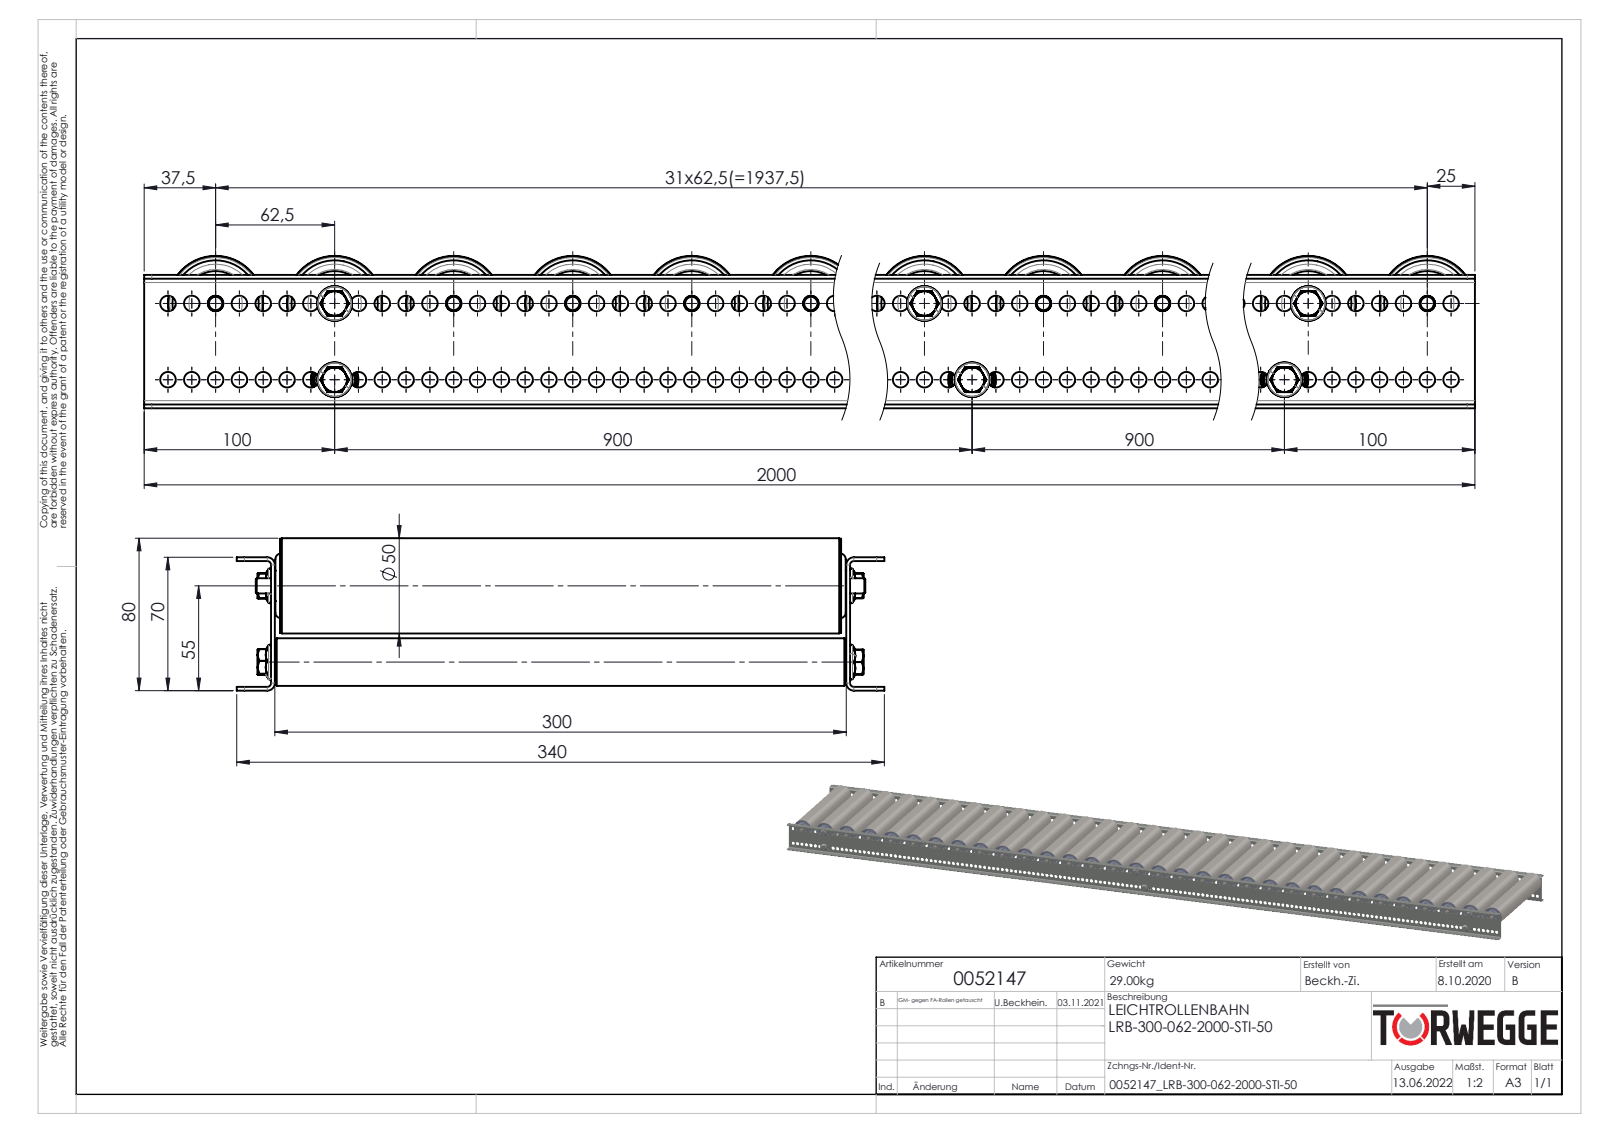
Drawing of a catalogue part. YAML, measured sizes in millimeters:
part_name: "Profil_LRB-20x70x20x2_KFG_S100202_U-PROFIL-20-70-20-2-LRB-L=2000; 0039771_Tragrollenrohr-Ø50x1,5STI_KFG_EL300; Druckfeder_1,2x10x30; 0026295_Typ-TRG_50x1,5-8 (+8 more)"
step_written_by: "SolidWorks 2020 (AUTOMOTIVE_DESIGN)"
units: millimeters
bodies: {solids: 728, faces: 12550, planar: 2508, cylindrical: 4480, other: 5562}
overall_size: [2000, 340, 80]
volume: 4202000
surface_area: 5008000
round_holes:
  - {diameter: 8.2, count: 318}
  - {diameter: 17.1, count: 32}
  - {diameter: 18.5, count: 32}
  - {diameter: 27.7, count: 32}
  - {diameter: 45.3, count: 32}
  - {diameter: 47, count: 32}
  - {diameter: 7.6, count: 29}
  - {diameter: 6.8, count: 6}
  - {diameter: 12, count: 3}
  - {diameter: 12.2, count: 3}
  - {diameter: 19.2, count: 3}
  - {diameter: 21, count: 3}
round_bosses_or_shafts:
  - {diameter: 8, count: 35}
  - {diameter: 50, count: 32}
  - {diameter: 49.5, count: 32}
  - {diameter: 47.3, count: 32}
  - {diameter: 29.7, count: 32}
  - {diameter: 27.4, count: 32}
  - {diameter: 27.3, count: 32}
  - {diameter: 16, count: 32}
partial_cylinders:
  - {radius: 0.6, count: 58}
  - {radius: 0.75, count: 58}
  - {radius: 2.45, count: 58}
  - {radius: 4.87, count: 29}
  - {radius: 7, count: 29}
  - {radius: 2.5, count: 12}
  - {radius: 4, count: 8}
  - {radius: 2, count: 4}
face_to_face_distances: [2, 302, 68, 300, 304, 70, 66, 1, 2.3, 301.7]
hole_center_spacings: [12.5, 25, 37.5, 50, 62.5, 75, 87.5, 100]
